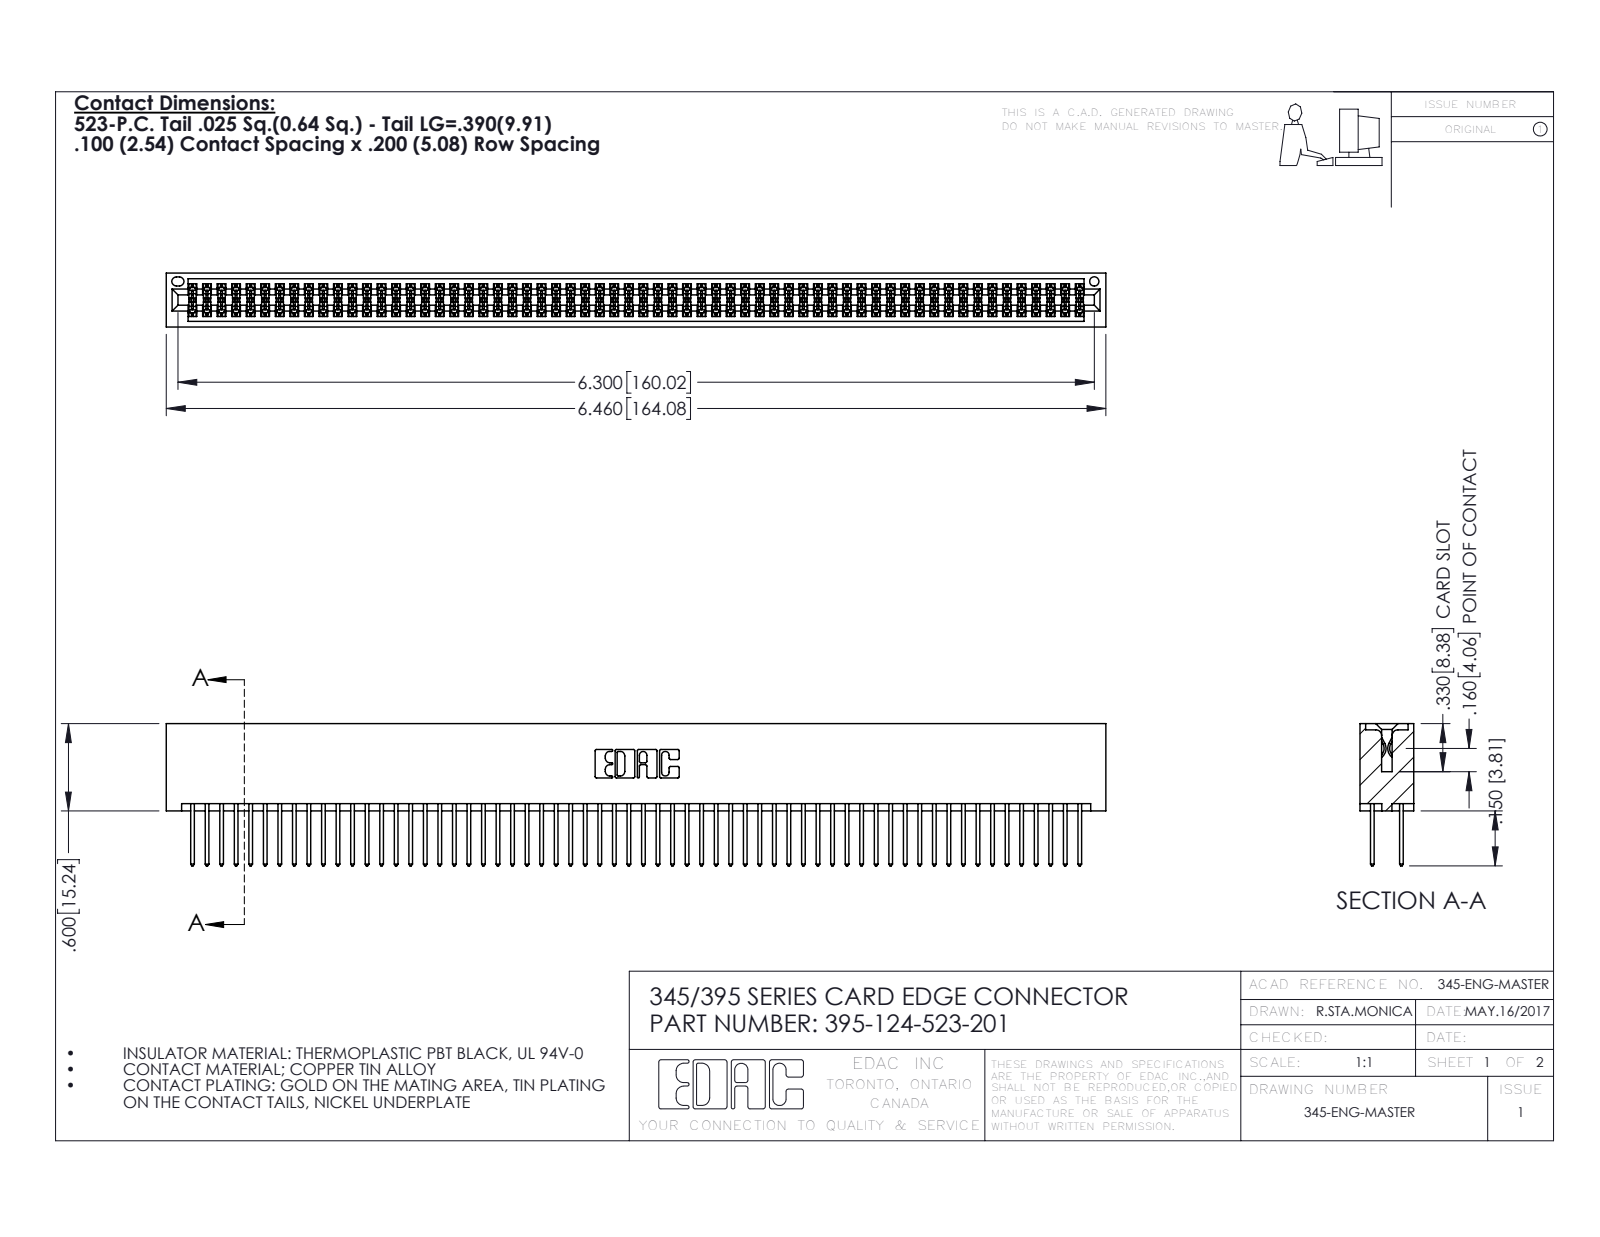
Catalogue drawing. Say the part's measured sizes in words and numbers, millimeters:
The part is named "395-124-523-201; 345 Part_No Mounting Lugs; 345-292-001_345-293-123". Its 3-D file was written by "SolidWorks 2016 (CONFIG_CONTROL_DESIGN)". It is 125 solids with 6318 faces: 4168 planar, 2150 cylindrical and 0 other. Overall it measures 164.1 by 24.8 by 9.4 millimeters. Its volume is 16 990 cubic millimeters and its surface area 26 950 square millimeters. Round holes: 1 of diameter 1.6. Partial cylindrical surfaces (rounded edges, fillets, slot ends): 186 of radius 0.2, 124 of radius 0.3, 22 of radius 0.3, 6 of radius 0.2, 6 of radius 0.8, 3 of radius 0.7, 2 of radius 0.4, 2 of radius 0.5. The main face-to-face distances are 7.6, 1.8, 5.1, 2.5, 6.9, 0.6, 9.4, 5.7, 4.4, 3.8.
